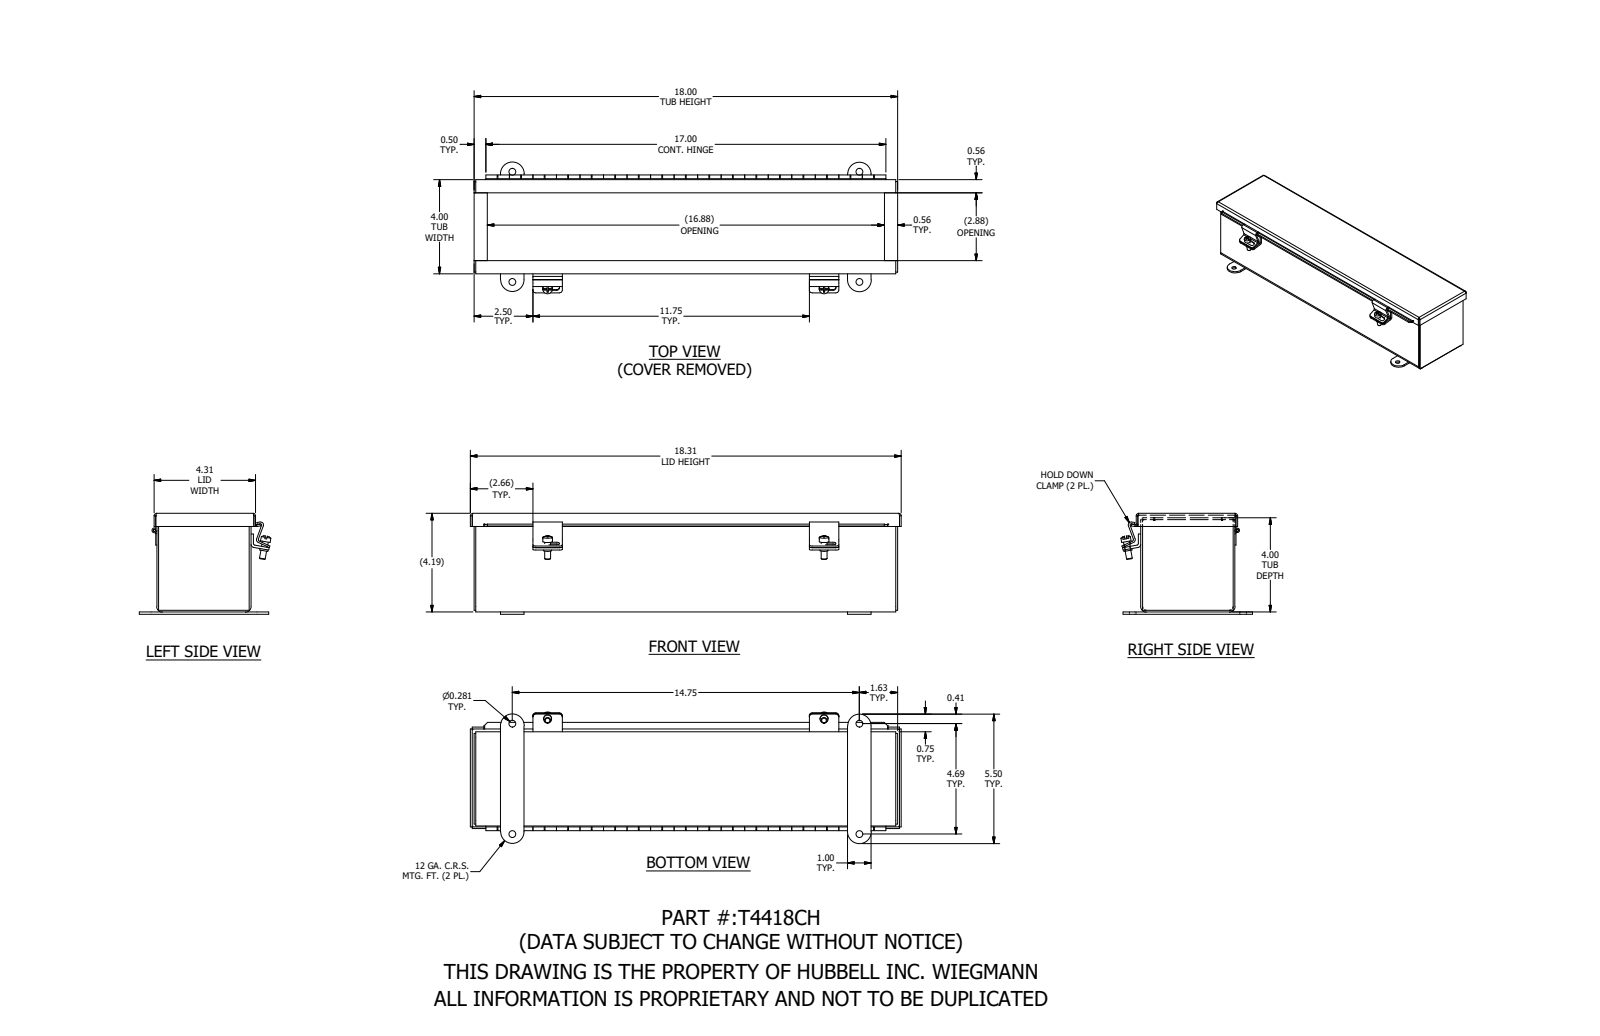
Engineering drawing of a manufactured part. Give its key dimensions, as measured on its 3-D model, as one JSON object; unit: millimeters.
{"part_name": "T4418CH", "step_written_by": "SolidWorks 2021 (AUTOMOTIVE_DESIGN)", "units": "millimeters", "bodies": {"solids": 15, "faces": 502, "planar": 268, "cylindrical": 216, "other": 18}, "overall_size": [465.2, 142.1, 108.8], "volume_mm3": 483900, "surface_area_mm2": 536400, "round_holes": [[7.1, 4], [5, 2], [2.9, 1]], "round_bosses_or_shafts": [[10.4, 2], [8.7, 2], [6.4, 2], [5.1, 1], [2.5, 1]], "partial_cylinders_radius": [[0.8, 9], [2.7, 9], [3.2, 8], [3.4, 4], [12.7, 4], [1.6, 3], [3.2, 3], [4, 2]], "face_to_face_distances": [1.9, 99.7, 104.5, 101.6, 97.8, 106.4, 102.6, 4.8, 102.7, 2.9], "hole_center_spacings": [119, 374.7, 393.1, 298.5]}
